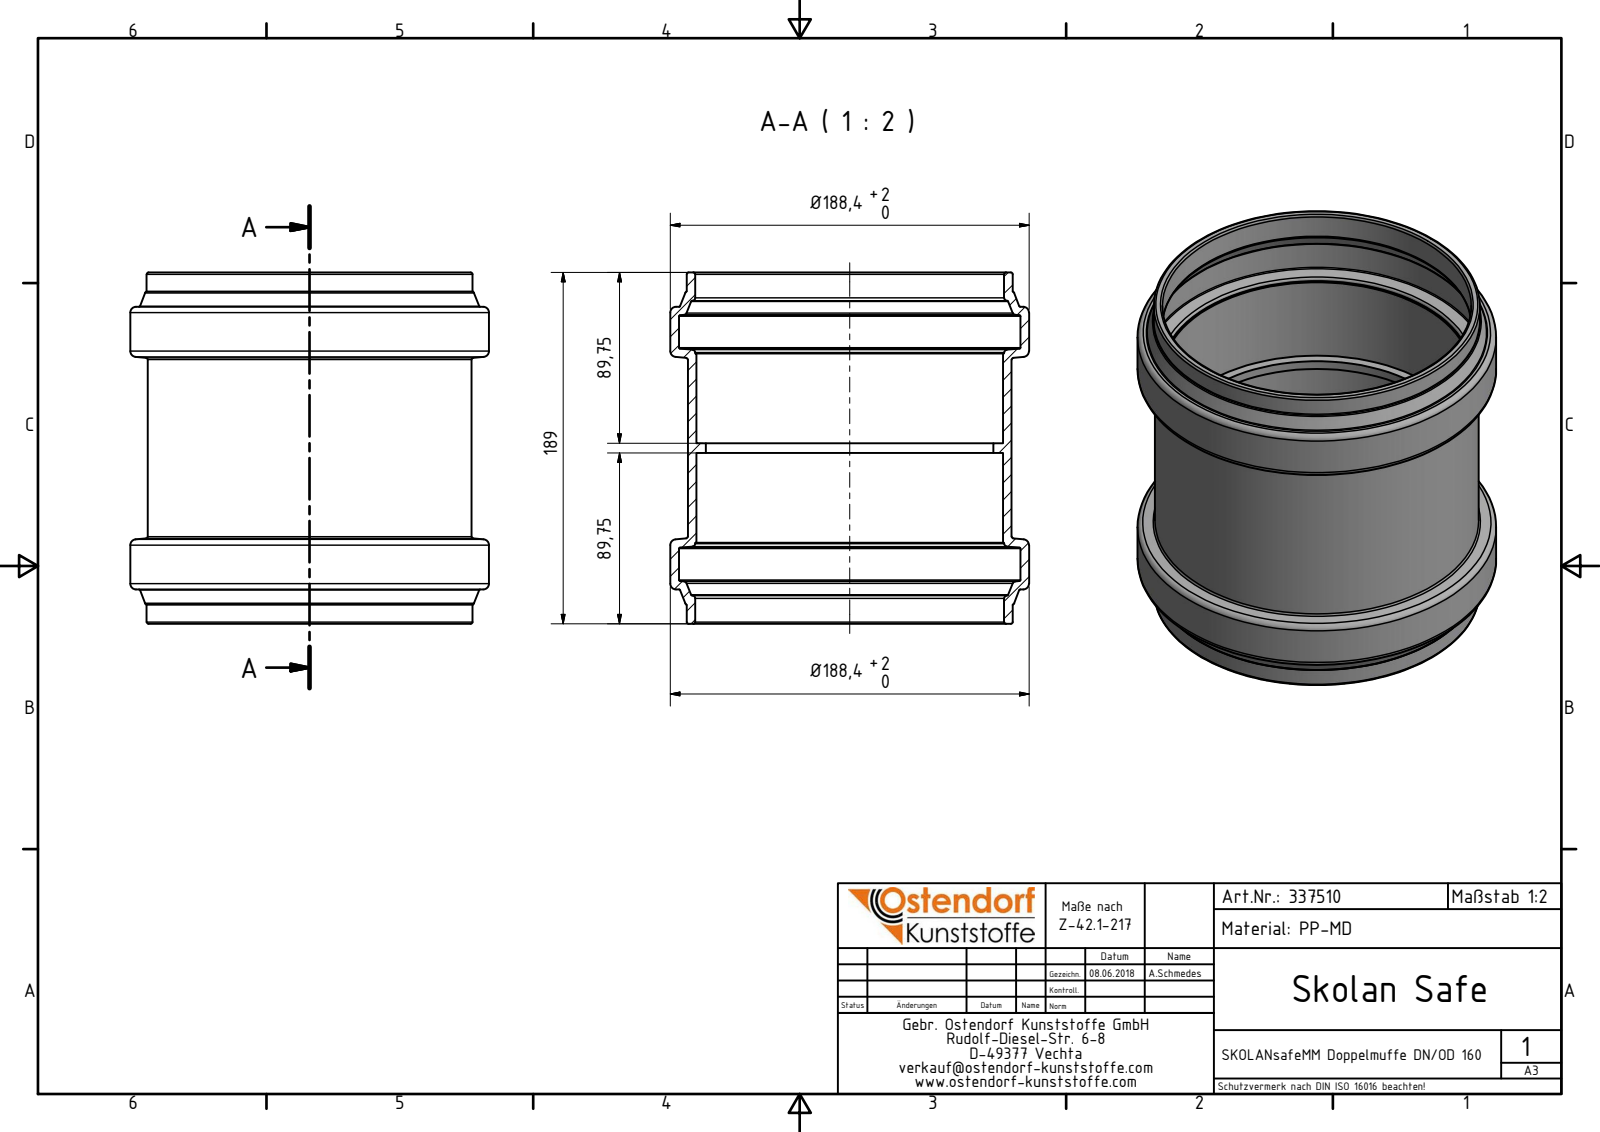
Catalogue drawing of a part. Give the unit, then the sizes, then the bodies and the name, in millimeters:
Units: millimetres
Overall size (bounding box): 188.4 × 188.4 × 184.5
Round holes (diameter × count): ⌀151 ×1, ⌀161 ×1, ⌀162.2 ×1, ⌀179.4 ×1
Round bosses / shafts (diameter × count): ⌀188.4 ×1, ⌀171.2 ×1, ⌀170 ×1
Main face-to-face distances: 89.75, 94.75, 5, 18.1, 166.4, 71.65, 76.65, 184.5, 148.3, 42.62
Volume: 522 316 mm³ · Surface area: 232 812 mm²
Bodies: 1 solid, 62 faces (8 planar, 14 cylindrical, 40 other)
Part name (STEP PRODUCT): 337510 SKOLANsafeMM Doppelmuffe DN_OD 160
STEP written by: Autodesk Inventor 2016 (AUTOMOTIVE_DESIGN)
